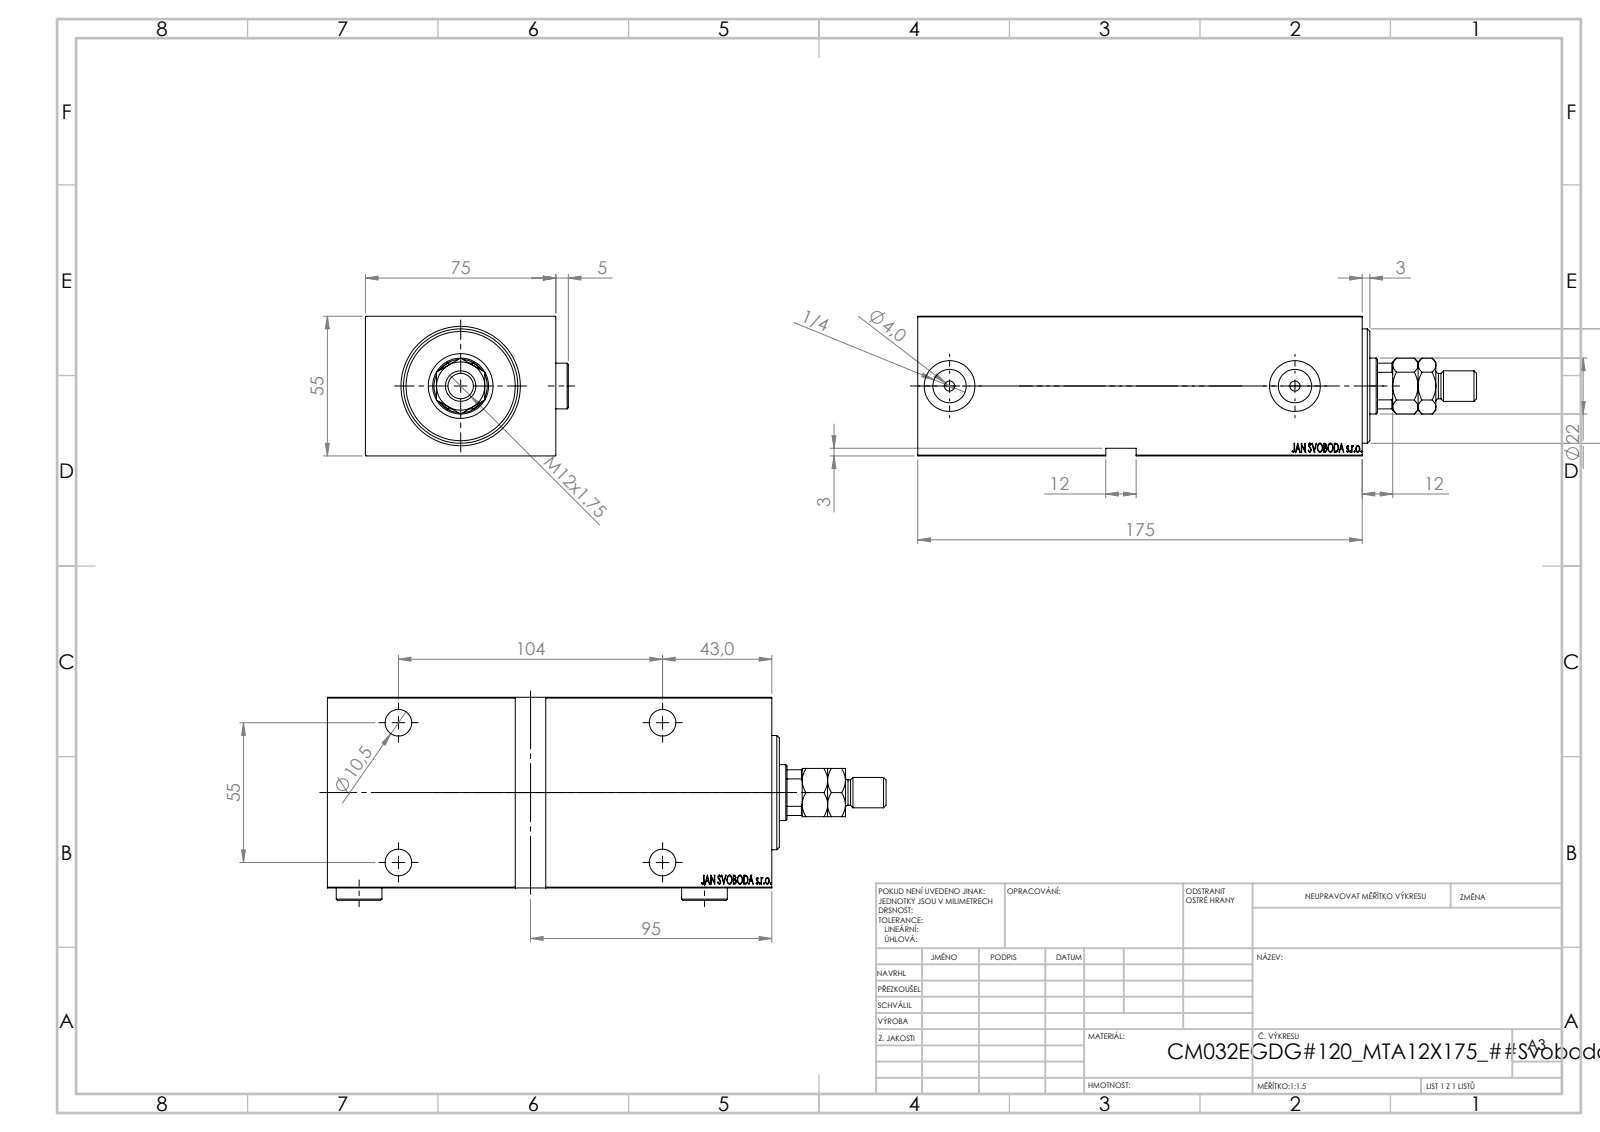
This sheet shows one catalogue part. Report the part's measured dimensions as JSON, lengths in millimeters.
{"part_name": "Zatka_OIL_PORT; MTA; V450CM_E_Body; V450CM_E_VCP (+1 more)", "step_written_by": "SolidWorks 2019 (CONFIG_CONTROL_DESIGN)", "units": "millimeters", "bodies": {"solids": 6, "faces": 958, "planar": 460, "cylindrical": 70, "other": 428}, "overall_size": [220, 79.9, 55], "volume_mm3": 651702, "surface_area_mm2": 106620, "round_holes": [[10.5, 5], [16.5, 4], [4, 2], [13.16, 2], [20, 2], [22, 1], [25.5, 1], [32, 1], [45, 1]], "round_bosses_or_shafts": [[18, 2], [34, 1], [12, 1], [10, 1]], "partial_cylinders_radius": [[10.5, 1]], "face_to_face_distances": [55, 75, 175, 3, 5, 10, 165, 170, 160, 74.9], "hole_center_spacings": [55, 104, 117.65, 136]}
